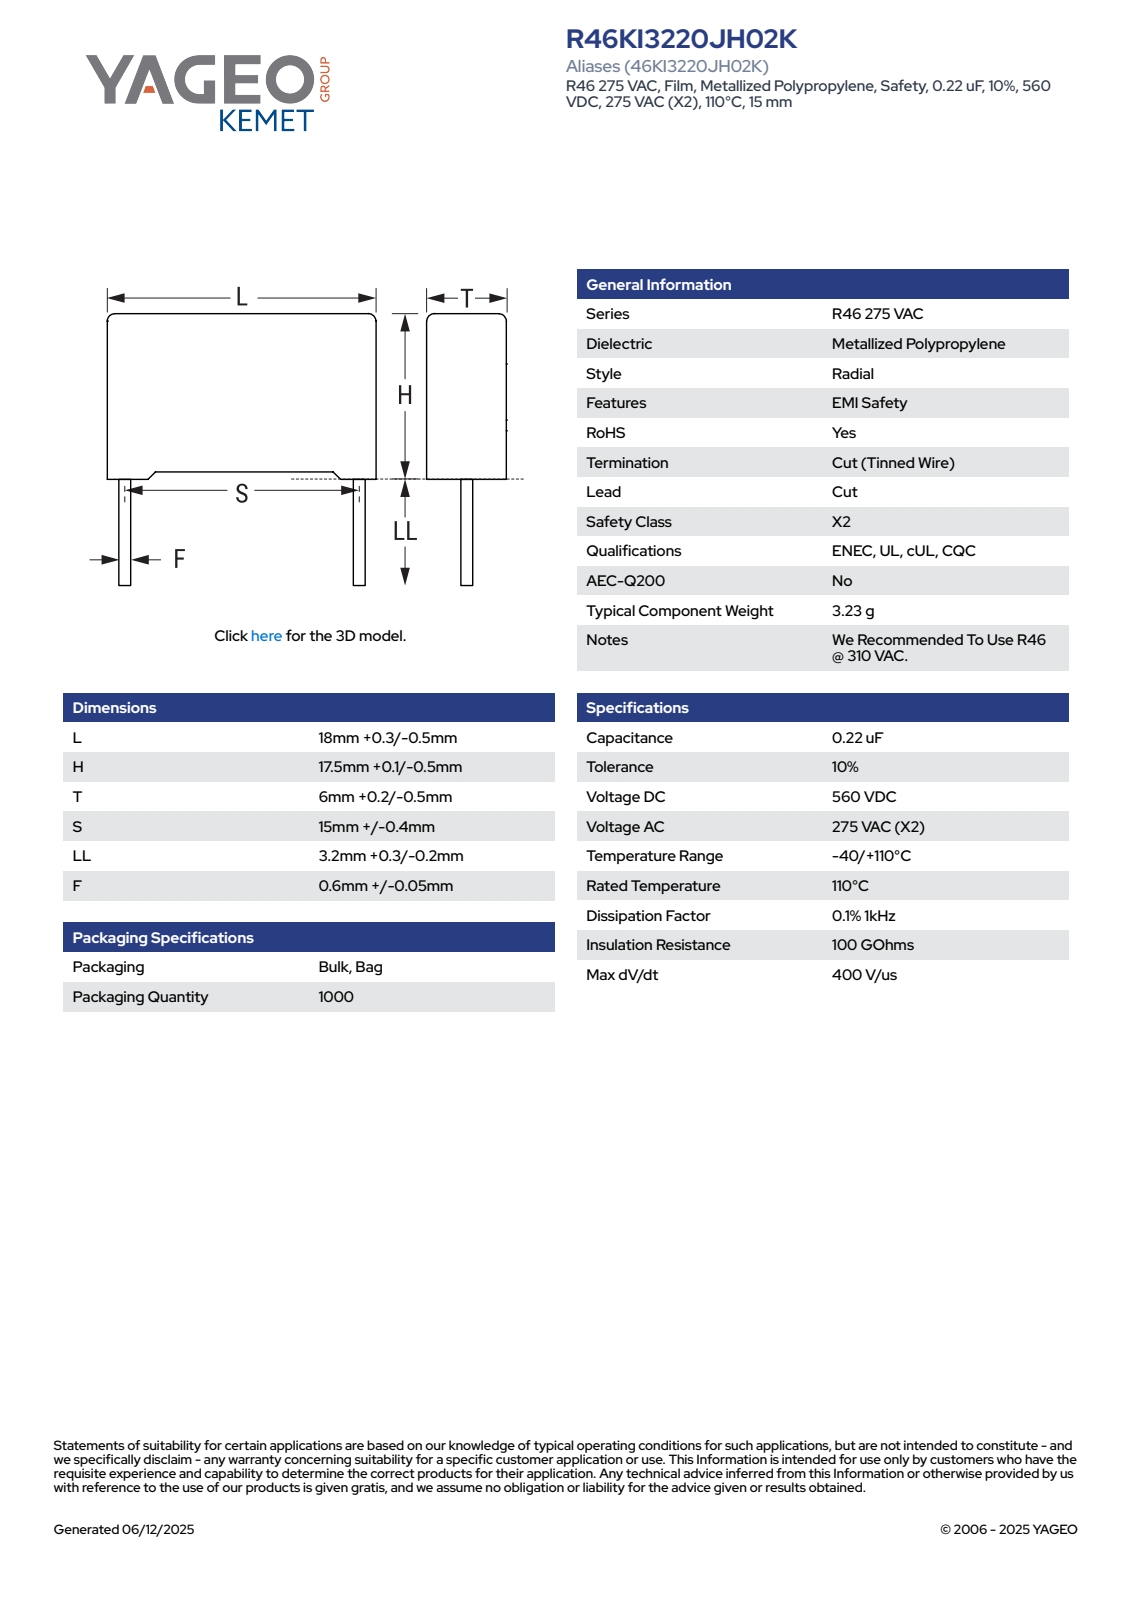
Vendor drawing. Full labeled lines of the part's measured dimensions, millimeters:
Part name (STEP PRODUCT): CFR_RB2_18X17.5X6_L18.3H17.6T6.2S15LL3.5F0.65
STEP written by: SolidWorks 2021 (AUTOMOTIVE_DESIGN)
Units: millimetres
Bodies: 4 solids, 85 faces (77 planar, 8 cylindrical, 0 other)
Overall size (bounding box): 21.1 × 18.3 × 6.21
Volume: 1 925 mm³ · Surface area: 1 127 mm²
Round bosses / shafts (diameter × count): ⌀0.65 ×2
Partial cylindrical surfaces — rounded edges, fillets, slot ends (radius × count): R0.5 ×4
Main face-to-face distances: 6.2, 18.3, 16.85, 0.61, 0.75, 17.6, 16.99, 5.59, 17.69, 4.98
